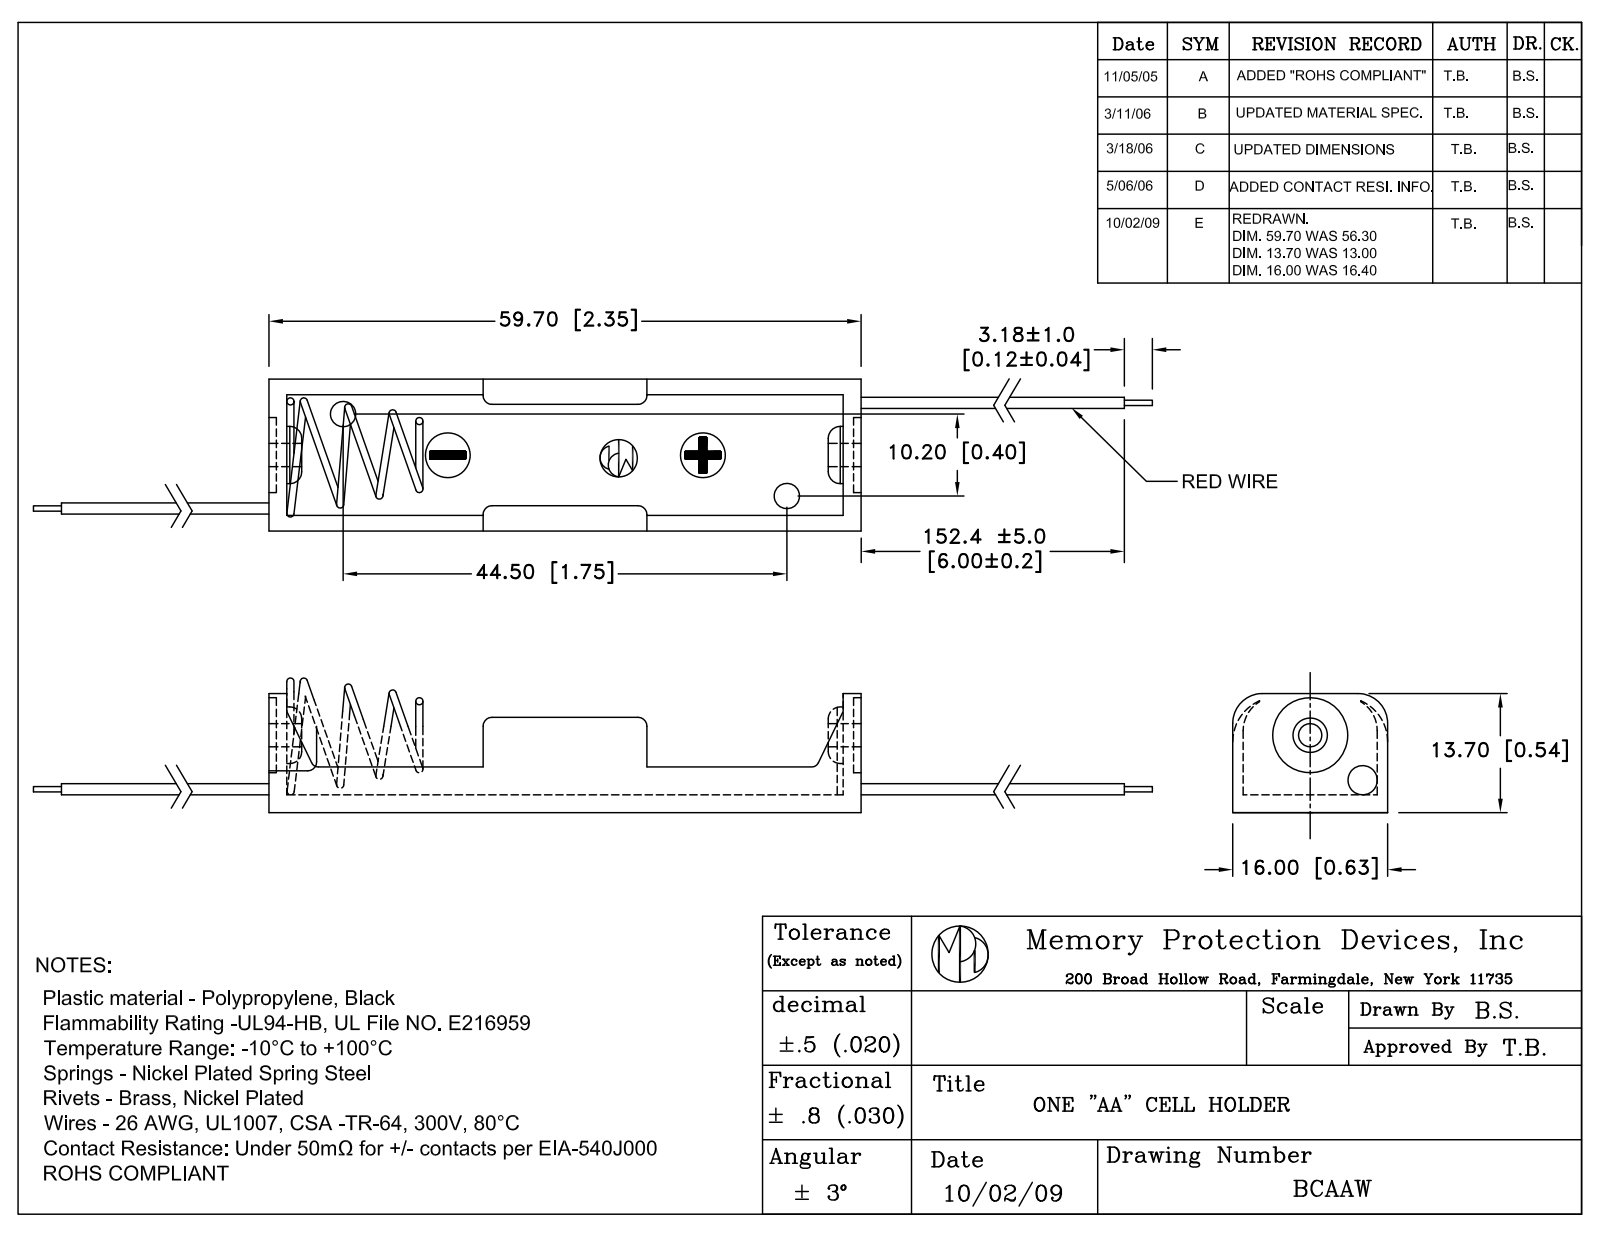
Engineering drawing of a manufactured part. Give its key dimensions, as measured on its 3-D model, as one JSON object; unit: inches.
{"part_name": "BCAAW", "step_written_by": "SolidWorks 2017 (AUTOMOTIVE_DESIGN)", "units": "inches", "bodies": {"solids": 7, "faces": 208, "planar": 79, "cylindrical": 83, "other": 46}, "overall_size": [14.776, 0.63, 0.539], "volume_in3": 0.176, "surface_area_in2": 10.01, "round_holes": [[0.1, 4], [0.016, 2], [0.063, 1], [0.091, 1], [0.118, 1], [0.315, 1]], "round_bosses_or_shafts": [[0.146, 2], [0.032, 2], [0.244, 1], [0.138, 1], [0.024, 1]], "partial_cylinders_radius": [[0.008, 12], [0.079, 4], [0.118, 2], [0.166, 2], [0.244, 2]], "face_to_face_distances": [0.043, 0.061, 0.587, 0.63, 2.307, 0.543, 2.264, 2.35, 0.012, 2.338], "hole_center_spacings": [0.322, 0.443, 1.797]}
